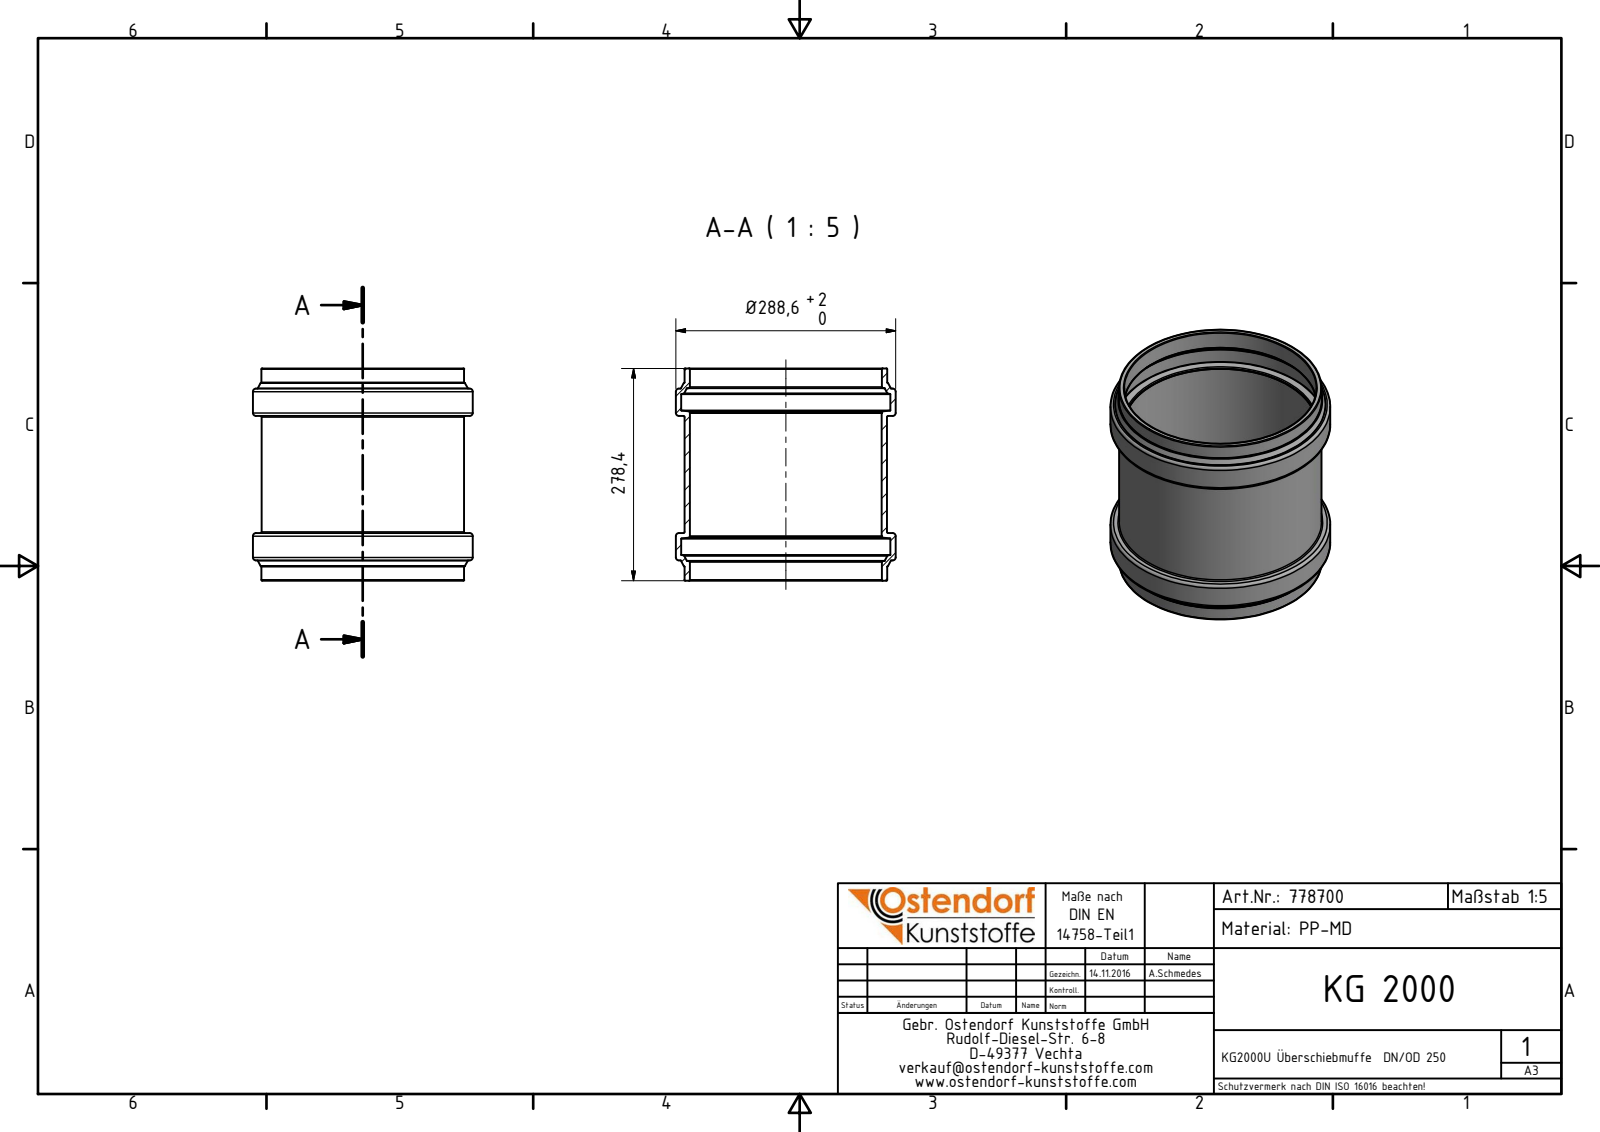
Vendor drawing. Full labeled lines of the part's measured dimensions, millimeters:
Part name (STEP PRODUCT): 778700 KG2000U Überschiebmuffe DN_OD 250
STEP written by: Autodesk Inventor 2016 (AUTOMOTIVE_DESIGN)
Units: millimetres
Bodies: 1 solid, 58 faces (8 planar, 12 cylindrical, 38 other)
Overall size (bounding box): 288.6 × 288.6 × 278.4
Volume: 1 825 000 mm³ · Surface area: 525 664 mm²
Round holes (diameter × count): ⌀251.7 ×1, ⌀252.1 ×1, ⌀274.6 ×1
Round bosses / shafts (diameter × count): ⌀288.6 ×1, ⌀266.1 ×1, ⌀265.7 ×1
Main face-to-face distances: 62.4, 216, 153.6, 278.4, 26.5, 251.9, 35.9, 189.5, 225.4, 58.41
